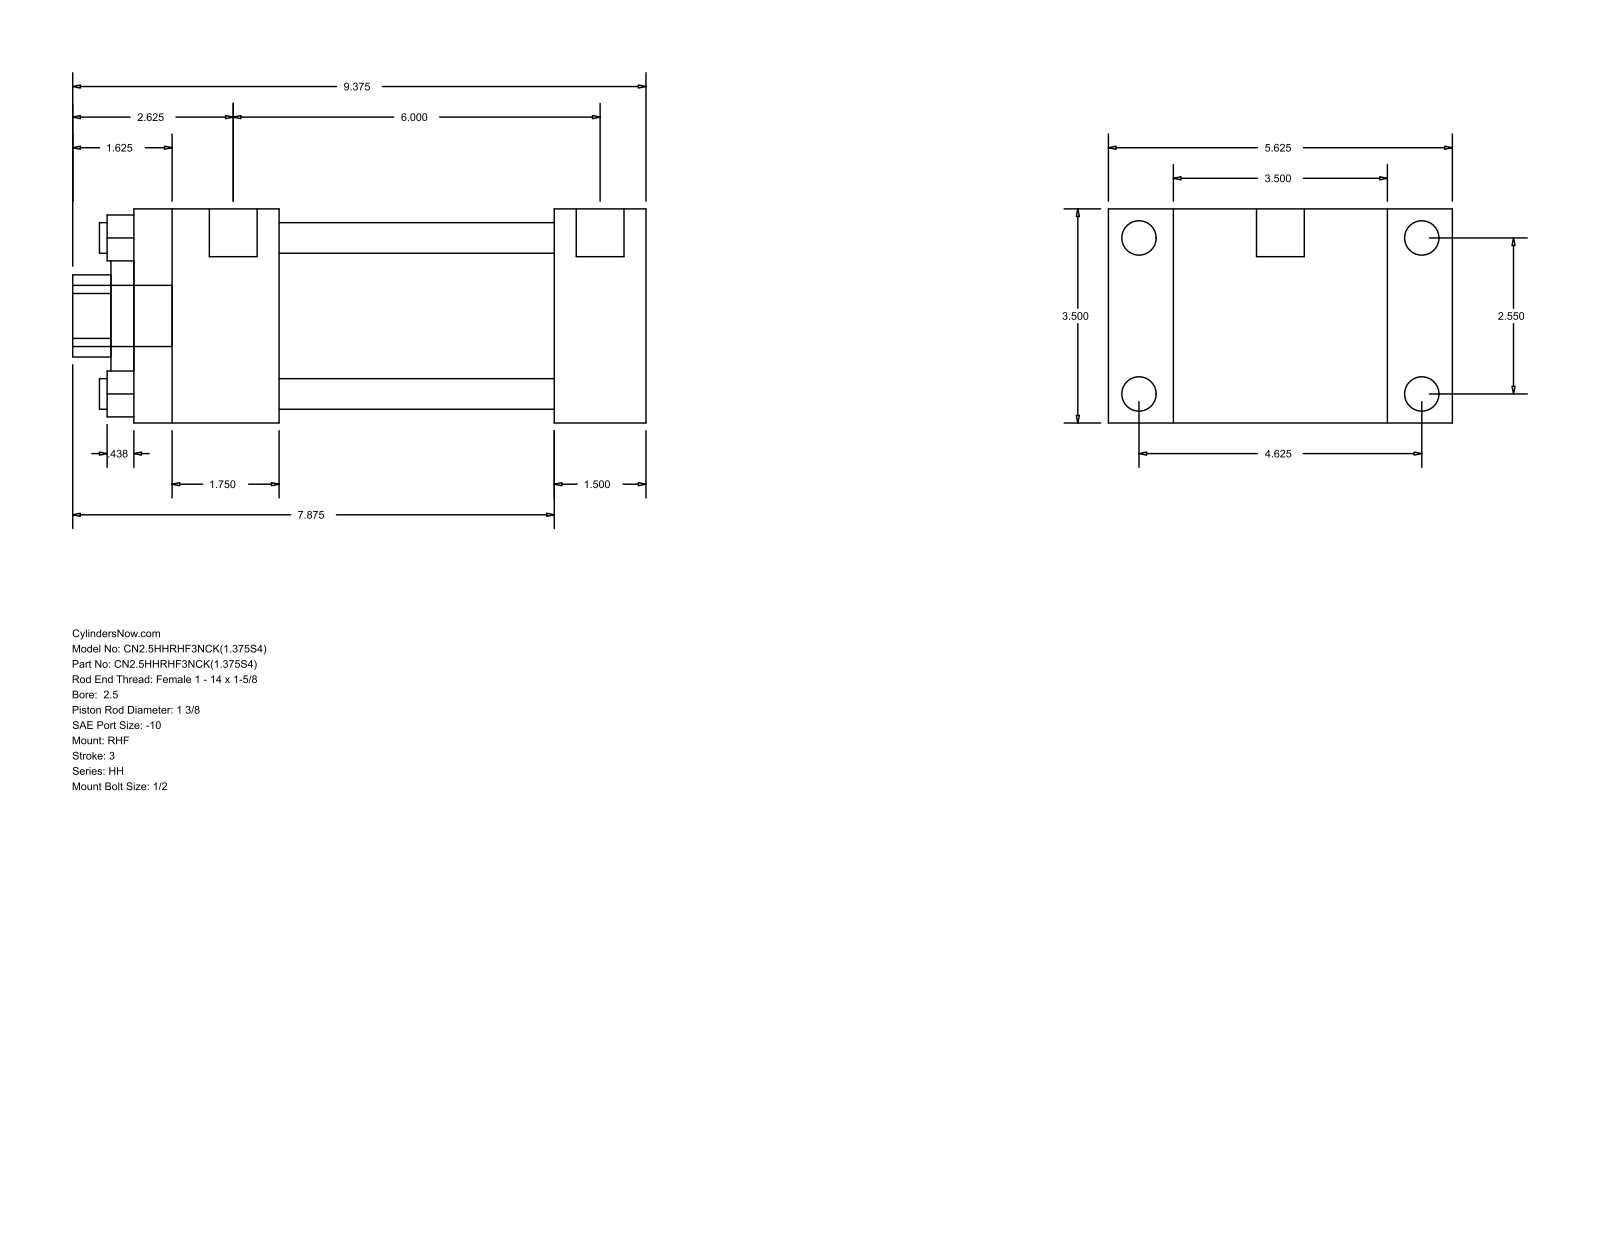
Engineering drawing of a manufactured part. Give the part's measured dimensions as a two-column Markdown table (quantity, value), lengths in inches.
| quantity | value |
| --- | --- |
| part name | HH_RHF__0250_1.375 |
| STEP written by | GSSL Pune (CONFIG_CONTROL_DESIGN) |
| units | inches |
| bodies | 0 solids, 88 faces (60 planar, 28 cylindrical, 0 other) |
| overall size | 9.375 × 5.625 × 3.5 |
| round holes (diameter × count) | 0.5 × 4, 1.375 × 1, 2 × 1, 2.875 × 1 |
| round bosses / shafts (diameter × count) | 0.563 × 4, 0.219 × 4, 0.781 × 2, 1 × 1 |
| partial cylindrical surfaces (radius × count) | 0.672 × 1 |
| main face-to-face distances | 3.5, 1.5, 1.063, 4.563, 6.875, 8.375, 5.625, 2.375, 4.5, 6 |
| hole center spacings | 1.803, 2.55, 3.606 |
